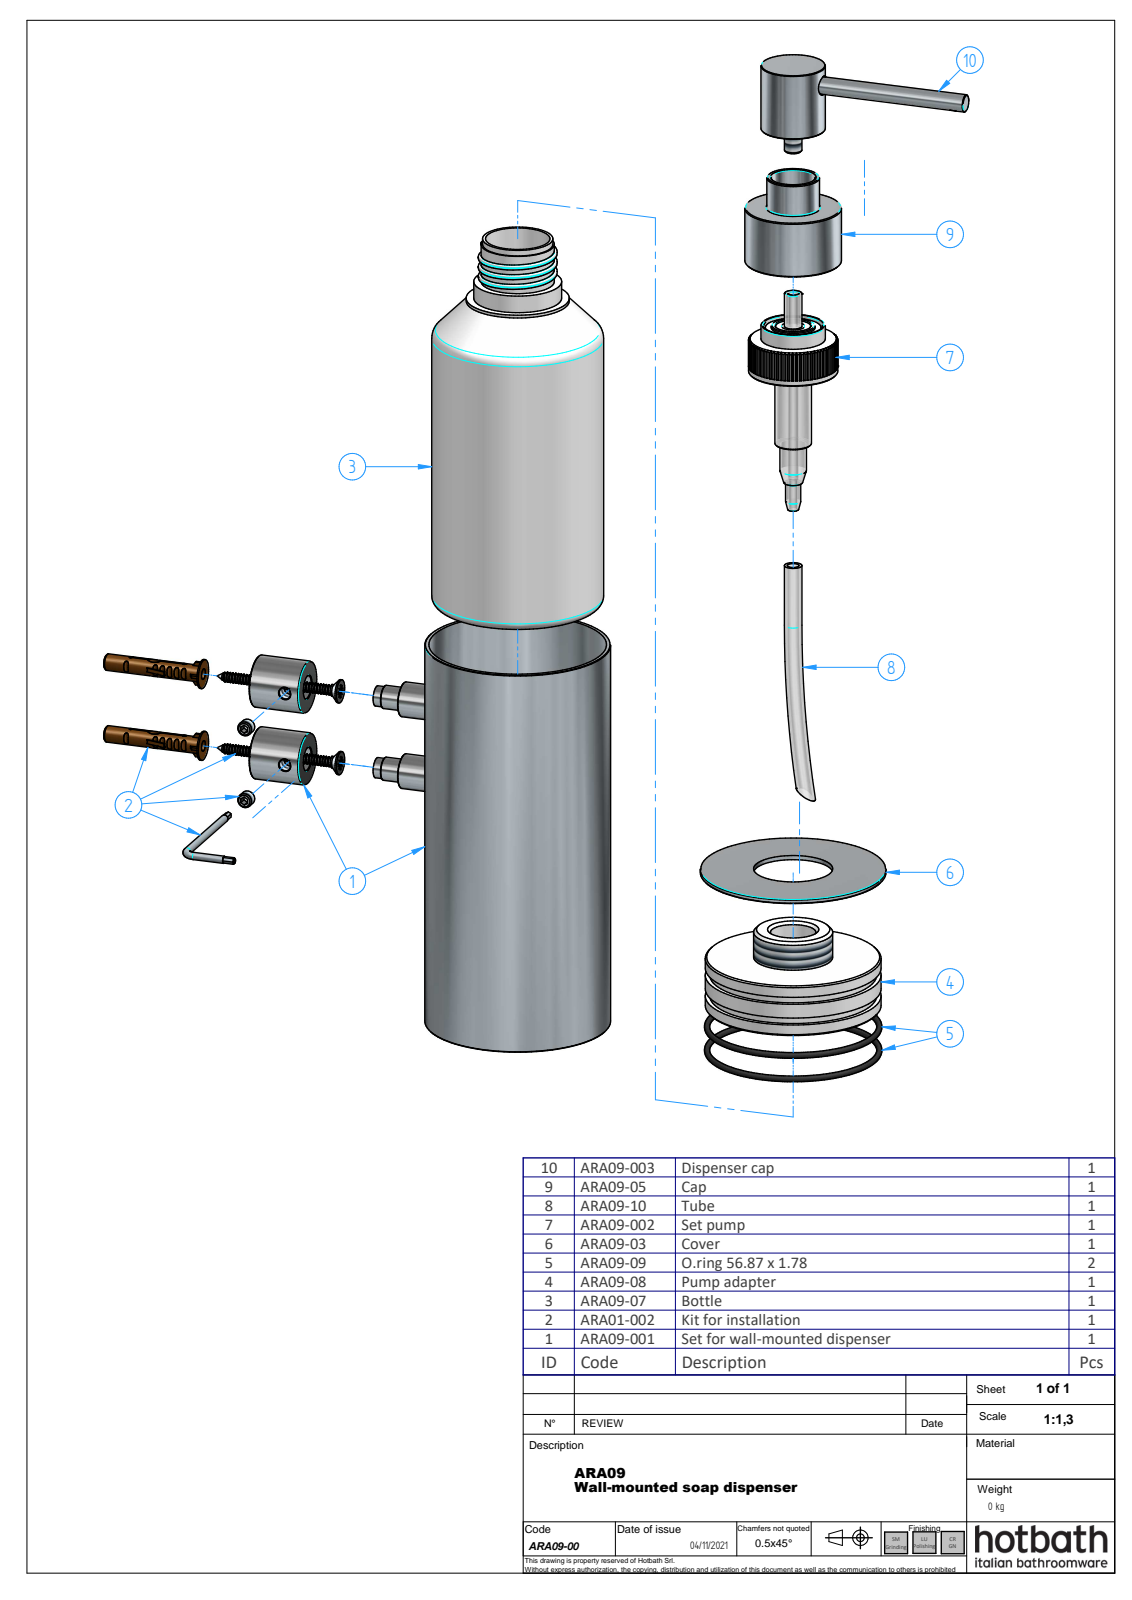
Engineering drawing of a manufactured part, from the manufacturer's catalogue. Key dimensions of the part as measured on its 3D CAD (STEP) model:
Part name (STEP PRODUCT): ARA09-00; ARA09-001_oa_0; ARA09-01; ARA09-02 (+8 more)
STEP written by: ST-DEVELOPER v16.7 (AP242_MANAGED_MODEL_BASED_3D_ENGINEERING_MIM_LF)
Units: millimetres
Bodies: 14 solids, 266 faces (119 planar, 85 cylindrical, 62 other)
Overall size (bounding box): 189 × 158.13 × 63.4
Volume: 66 370 mm³ · Surface area: 84 471 mm²
Round holes (diameter × count): ⌀4.13 ×3, ⌀1 ×2, ⌀1.7 ×2, ⌀3.24 ×2, ⌀3.5 ×2, ⌀3.7 ×2, ⌀4.2 ×2, ⌀4.92 ×2, ⌀8 ×2, ⌀2.5 ×1, ⌀6.2 ×1, ⌀15 ×1
Round bosses / shafts (diameter × count): ⌀18 ×3, ⌀5 ×3, ⌀12 ×2, ⌀10 ×2, ⌀6 ×2, ⌀5.7 ×2, ⌀60.5 ×1, ⌀33 ×1
Partial cylindrical surfaces — rounded edges, fillets, slot ends (radius × count): R0.8 ×12
Main face-to-face distances: 1.5, 136.5, 138, 135, 157.5, 156, 21, 19.5, 155.5, 154
Hole centre spacings: 26, 19.5, 58.5, 66.63, 71.5, 86.13, 97.5, 125.13
